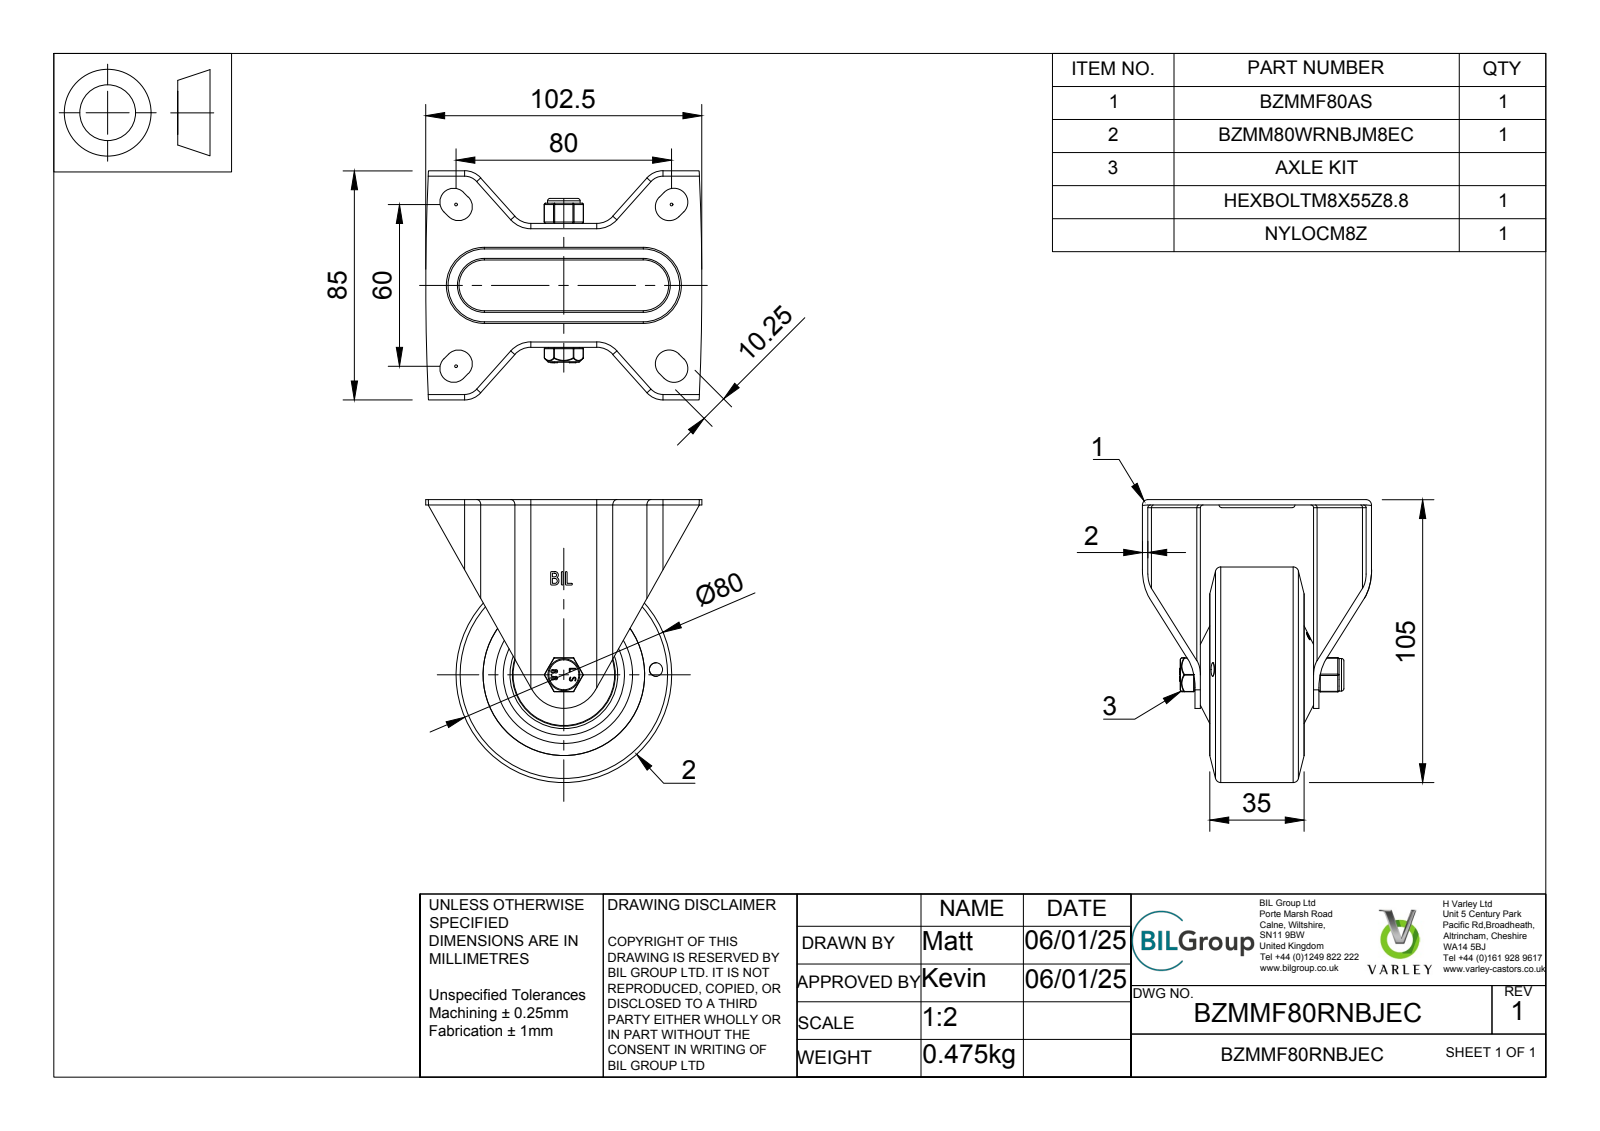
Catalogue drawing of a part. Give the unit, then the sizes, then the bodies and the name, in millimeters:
Units: millimetres
Overall size (bounding box): 105 × 102.5 × 85
Round holes (diameter × count): ⌀0.66 ×2, ⌀3 ×2, ⌀5 ×1, ⌀8 ×1, ⌀8.2 ×1, ⌀8.25 ×1, ⌀8.6 ×1, ⌀15 ×1, ⌀20 ×1, ⌀22.5 ×1, ⌀26 ×1, ⌀30 ×1
Round bosses / shafts (diameter × count): ⌀80 ×1, ⌀45 ×1, ⌀38.25 ×1, ⌀35 ×1, ⌀30.5 ×1, ⌀28 ×1, ⌀23 ×1, ⌀19.5 ×1
Partial cylindrical surfaces — rounded edges, fillets, slot ends (radius × count): R0.5 ×18, R0.25 ×12, R1 ×12, R2 ×8, R4 ×8, R5.12 ×8, R8 ×8, R0.33 ×4
Main face-to-face distances: 2, 44, 5.16, 5.5, 46, 10.5, 42, 26.5, 3.16, 17.5
Hole centre spacings: 3.22, 2.49
Volume: 182 782 mm³ · Surface area: 95 630 mm²
Bodies: 24 solids, 780 faces (282 planar, 227 cylindrical, 271 other)
Part name (STEP PRODUCT): BZMMF80RNBJEC v3; BZMMF80AS - 42 v2; ZINC PLATED, PRESSED STEEL BRACKET; BZMM80WRNBJEC v1 (+8 more)
STEP written by: Autodesk Translation Framework v13.20.0.188 (AP242_MANAGED_MODEL_BASED_3D_ENGINEERING_MIM_LF)
